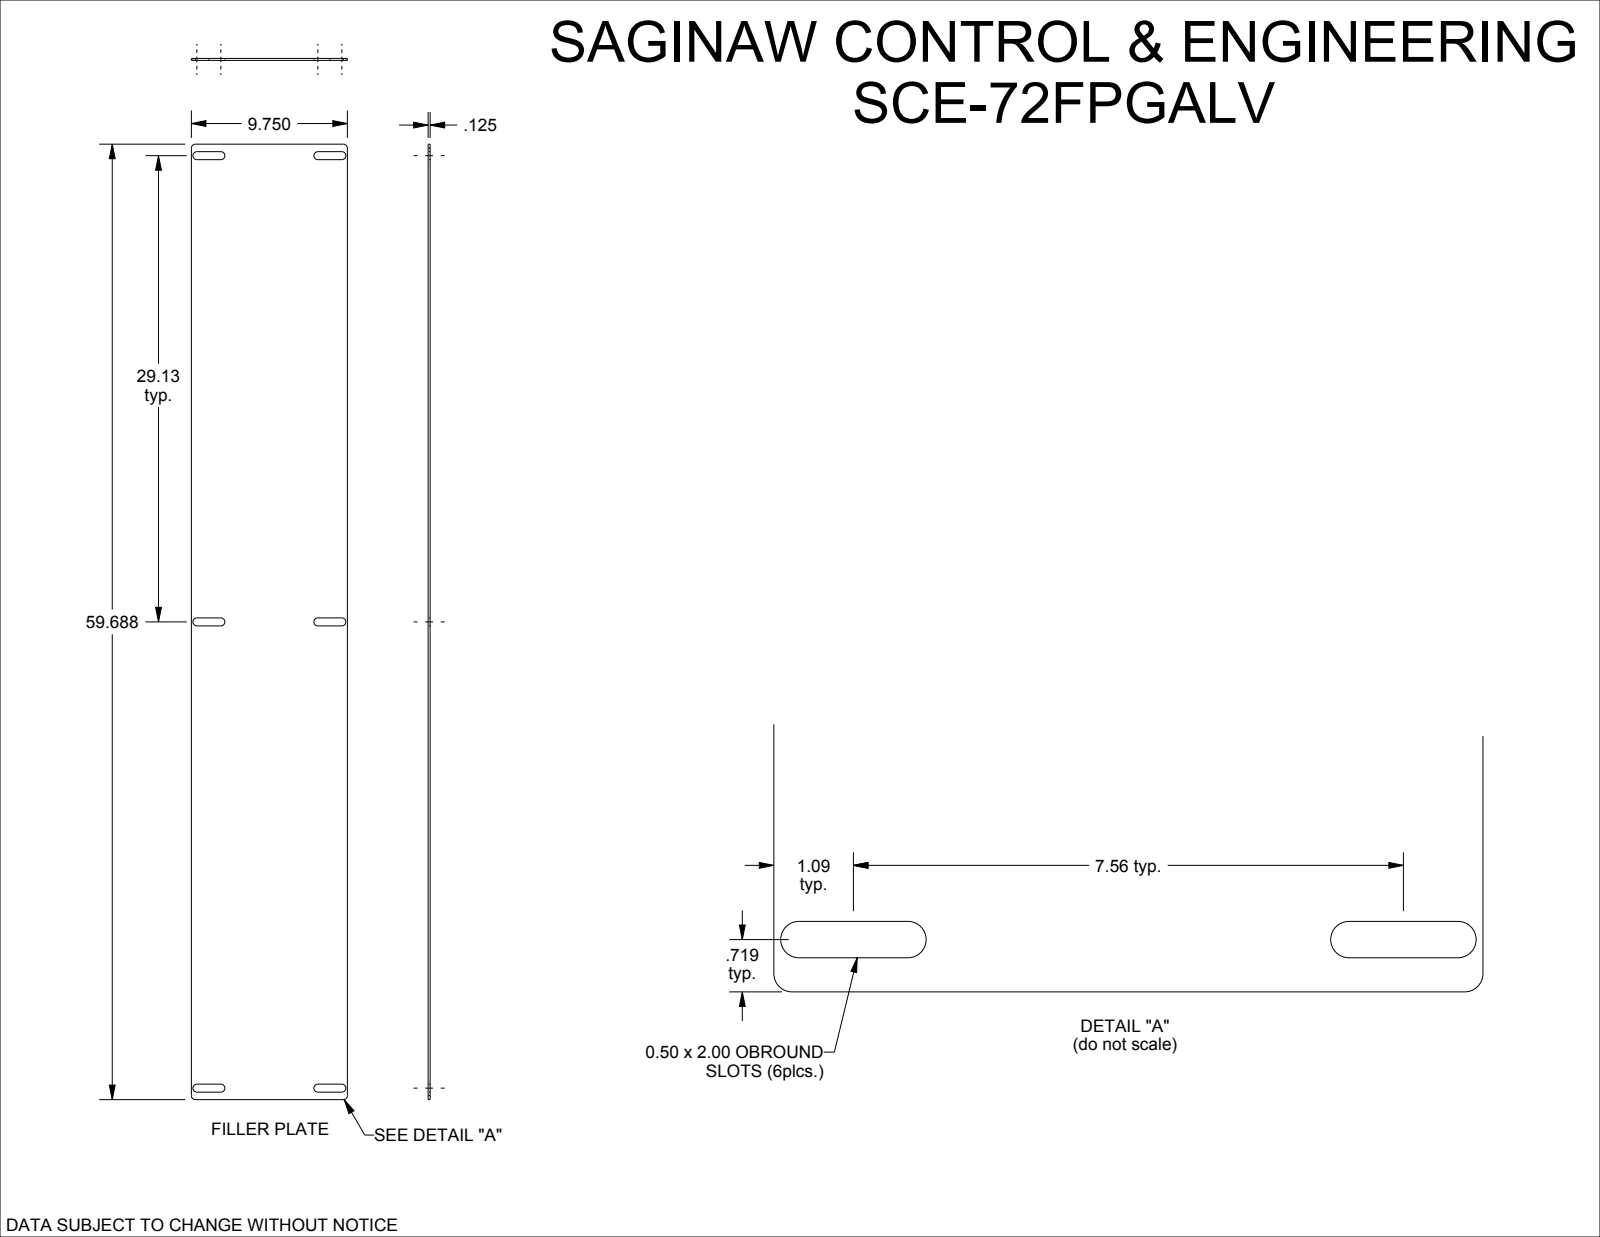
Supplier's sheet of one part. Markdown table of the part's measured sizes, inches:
| quantity | value |
| --- | --- |
| part name | SCE-72FPGALV |
| STEP written by | SolidWorks 2023 (AUTOMOTIVE_DESIGN) |
| units | inches |
| bodies | 1 solid, 46 faces (30 planar, 16 cylindrical, 0 other) |
| overall size | 59.687 × 9.75 × 0.125 |
| volume | 72.03 in³ |
| surface area | 1 173 in² |
| partial cylindrical surfaces (radius × count) | 0.25 × 16 |
| main face-to-face distances | 0.125, 9.75, 29.125, 59.687, 0.5, 29.594, 30.094, 0.469, 0.969, 58.719 |
